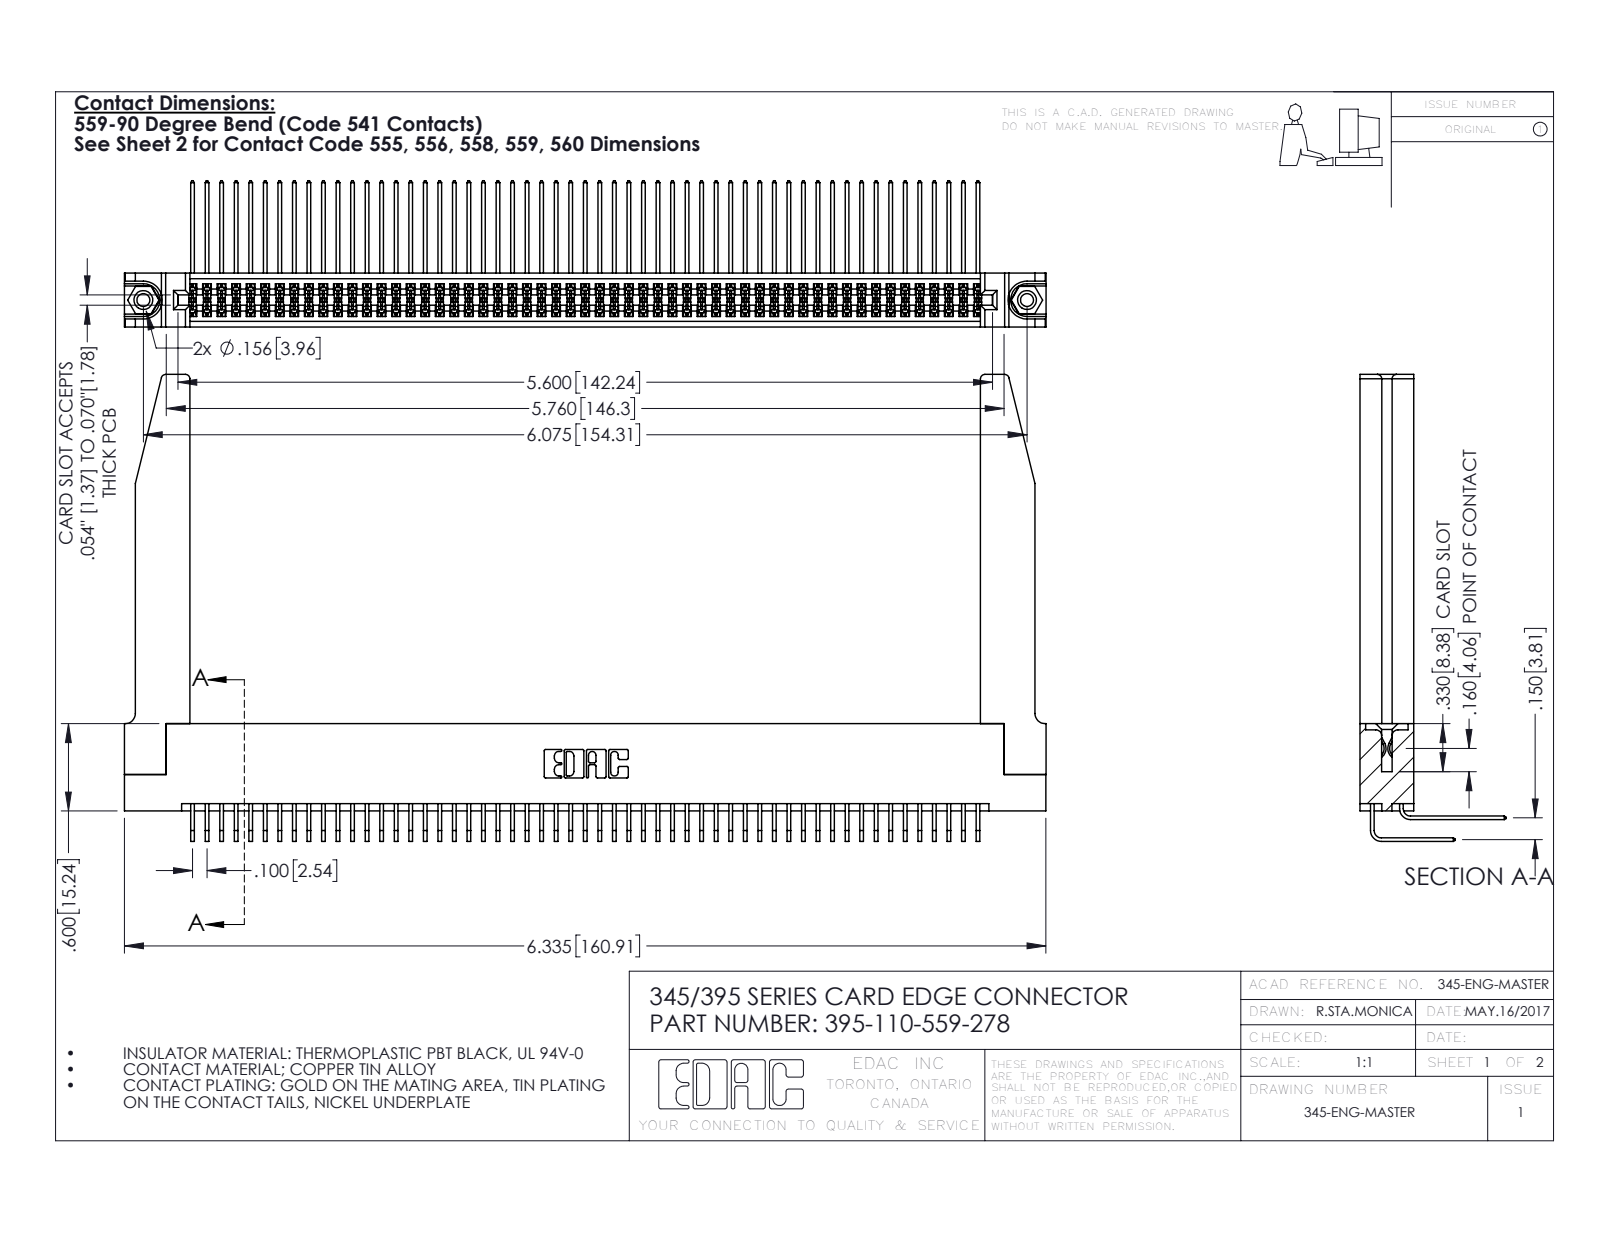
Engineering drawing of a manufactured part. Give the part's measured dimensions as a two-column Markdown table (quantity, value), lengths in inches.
| quantity | value |
| --- | --- |
| part name | 345-250-001_345-250-001-102; 345-292-001_558 559 Tail - 1; 345 Part_Flush Mounting Lugs - 0.156 Dia-TH; 345-292-001_559 Tail - 2 (+2 more) |
| STEP written by | SolidWorks 2016 (CONFIG_CONTROL_DESIGN) |
| units | inches |
| bodies | 115 solids, 6080 faces (4072 planar, 1956 cylindrical, 52 other) |
| overall size | 6.336 × 3.209 × 1.005 |
| volume | 1.474 in³ |
| surface area | 53.16 in² |
| round holes (diameter × count) | 0.089 × 2, 0.125 × 2, 0.156 × 2, 0.064 × 1 |
| round bosses / shafts (diameter × count) | 0.155 × 2 |
| partial cylindrical surfaces (radius × count) | 0.006 × 165, 0.01 × 22, 0.03 × 8, 0.007 × 6, 0.031 × 6, 0.026 × 3, 0.014 × 2, 0.019 × 2 |
| main face-to-face distances | 0.072, 0.298, 0.37, 0.2, 0.098, 0.272, 0.025, 0.225, 0.175, 0.15 |
| hole center spacings | 0.27, 5.839, 6.075 |
